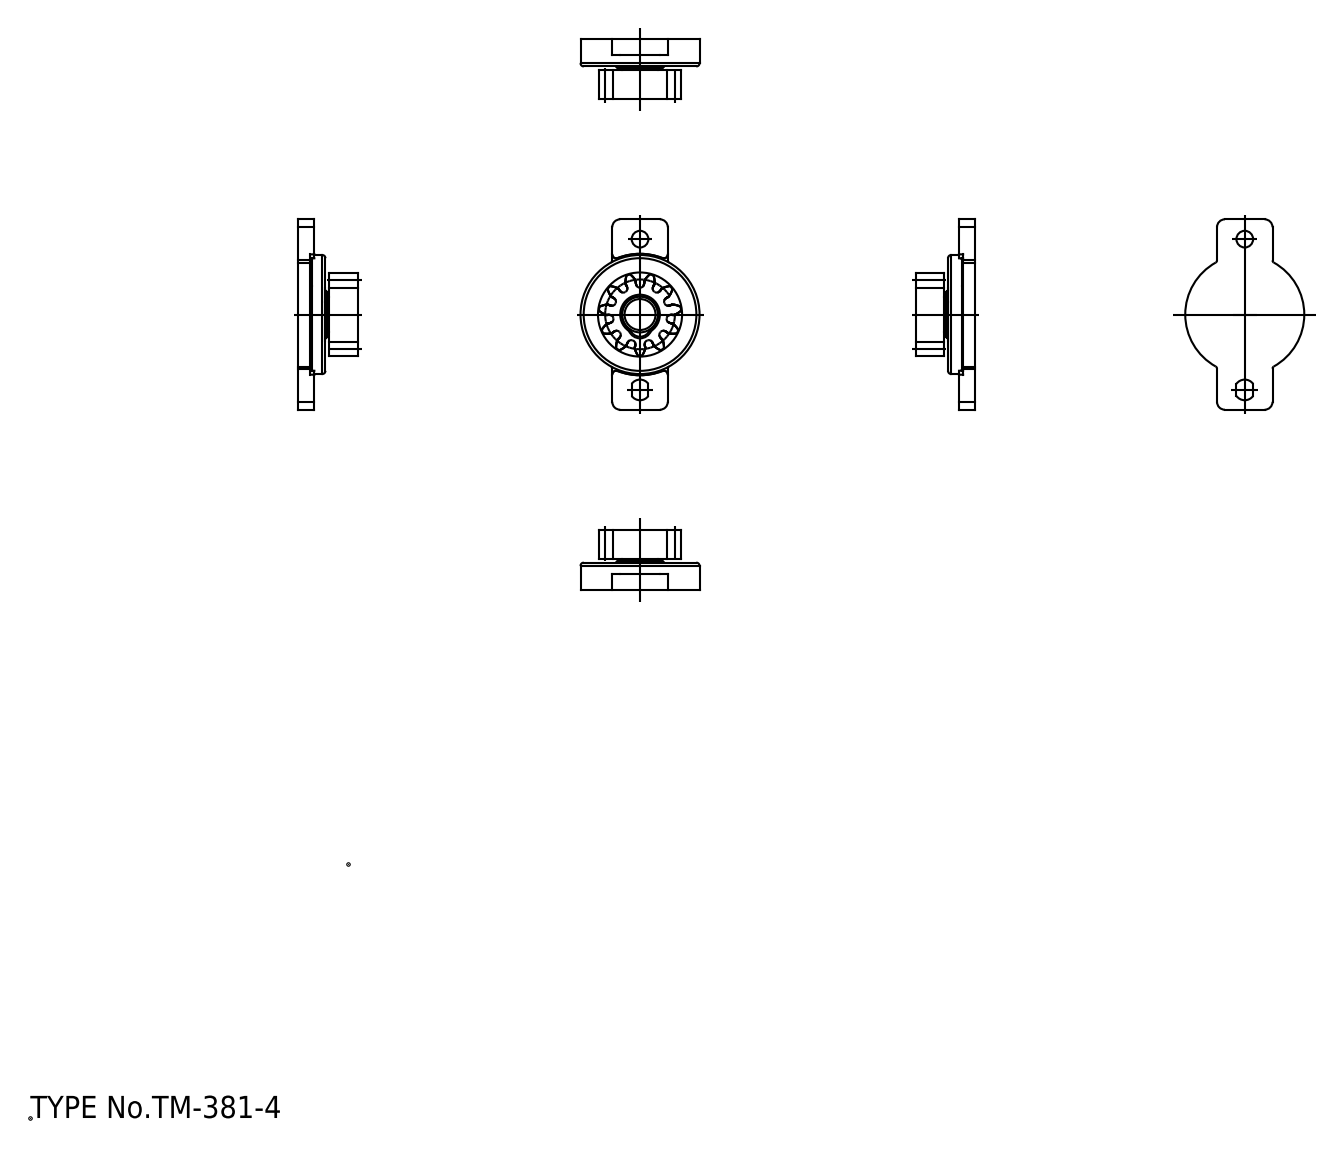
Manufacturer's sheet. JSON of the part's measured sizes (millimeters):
{"step_written_by": "spGate 19.8.4 (****-****-****-****) (AUTOMOTIVE_DESIGN)", "units": "millimeters", "bodies": {"solids": 1, "faces": 644, "planar": 568, "cylindrical": 68, "other": 8}, "overall_size": [24, 15, 7.5], "volume_mm3": 919, "surface_area_mm2": 1001, "round_holes": [[2.1, 1]], "round_bosses_or_shafts": [[15, 1], [4.5, 1]], "partial_cylinders_radius": [[0.4, 22], [0.3, 4], [0.5, 4], [1, 4], [1.3, 2], [3.4, 1], [5.2, 1], [7.66, 1]], "face_to_face_distances": [3.4, 1.4, 2, 0.5, 1.9, 3.9, 3.6, 4.1, 5.5, 7.5]}
